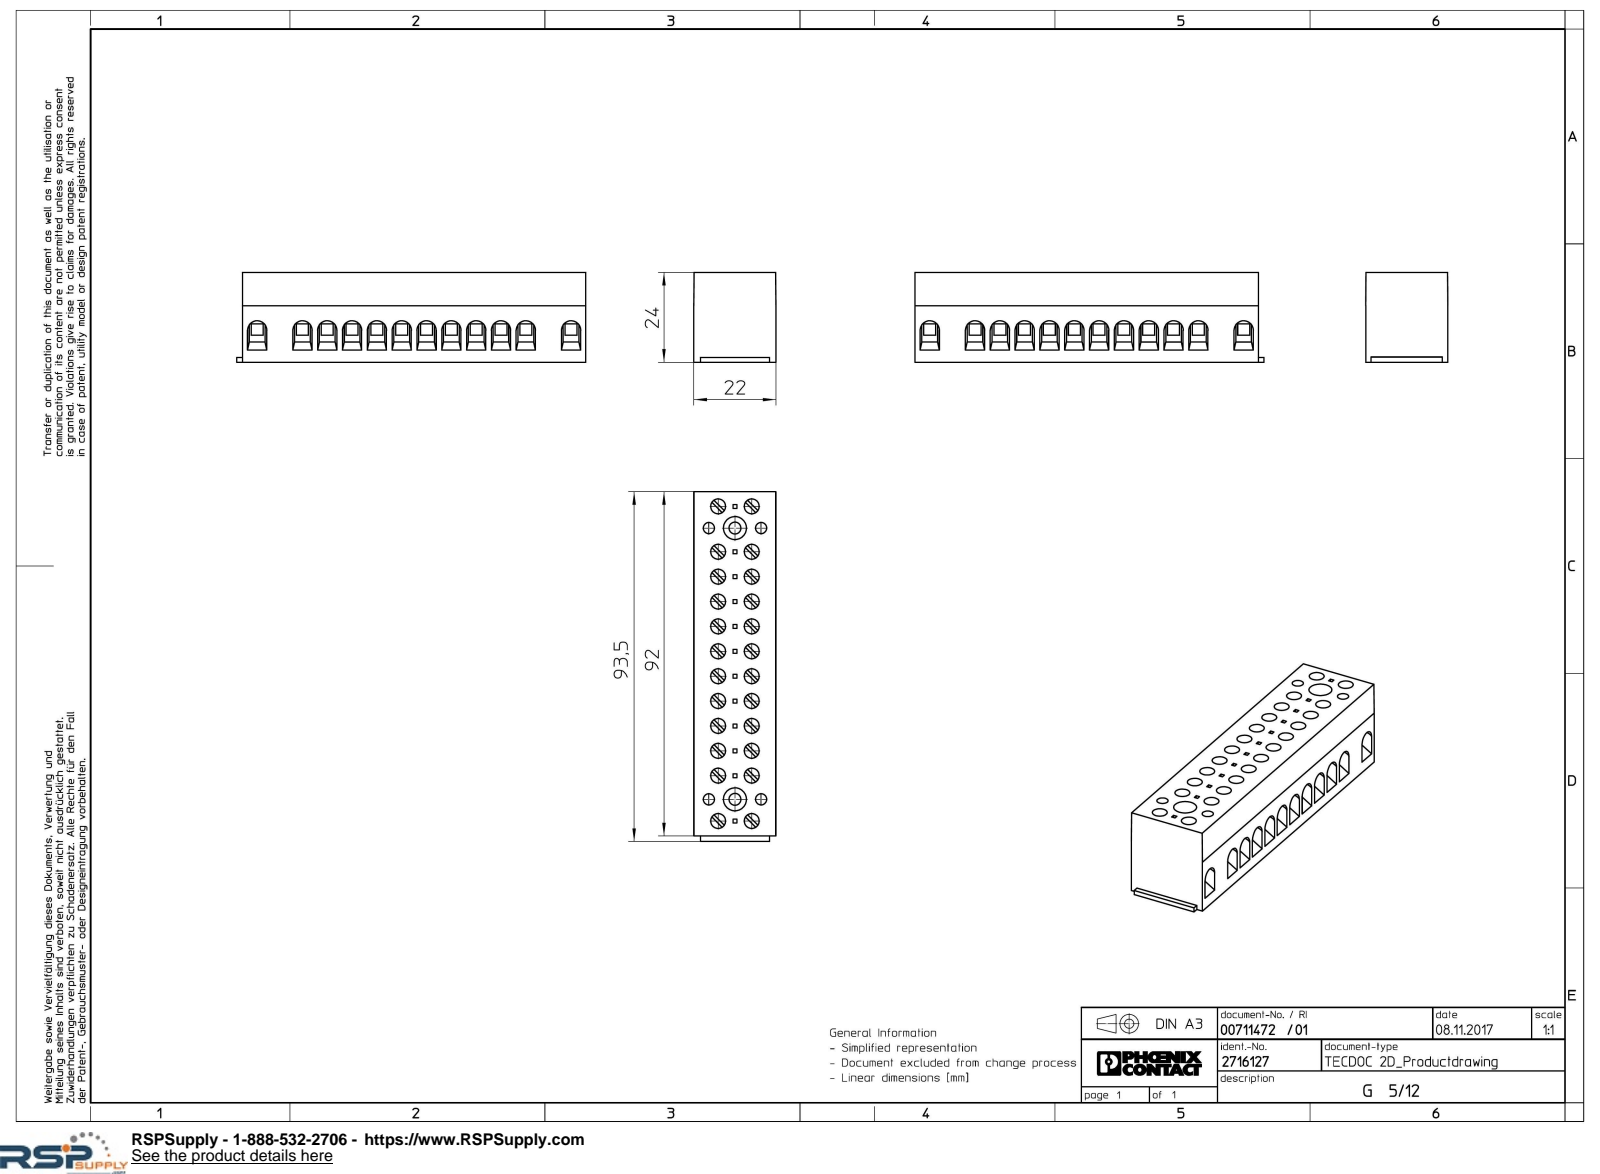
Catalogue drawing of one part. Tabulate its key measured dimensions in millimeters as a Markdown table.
| quantity | value |
| --- | --- |
| part name | G5_12-select |
| STEP written by | Creo Elements/Direct Modeling 20.1A 29-Sep-2018 (C) Parametric Technology GmbH (AUTOMOTIVE_DESIGN) |
| units | millimeters |
| bodies | 1 solid, 613 faces (497 planar, 116 cylindrical, 0 other) |
| overall size | 93.5 × 24 × 22 |
| volume | 40 572 mm³ |
| surface area | 15 872 mm² |
| round holes (diameter × count) | 4 × 24, 3 × 4, 3.2 × 2, 6.16 × 2 |
| round bosses / shafts (diameter × count) | 5 × 2 |
| partial cylindrical surfaces (radius × count) | 2.58 × 12, 0.8 × 2 |
| main face-to-face distances | 23, 22, 3.04, 92, 6.18, 16.82, 9.22, 13.78, 6.55, 13.3 |
| hole center spacings | 6.65, 11.19, 13.3, 16.06, 19.95, 21.89, 9, 26.6 |
